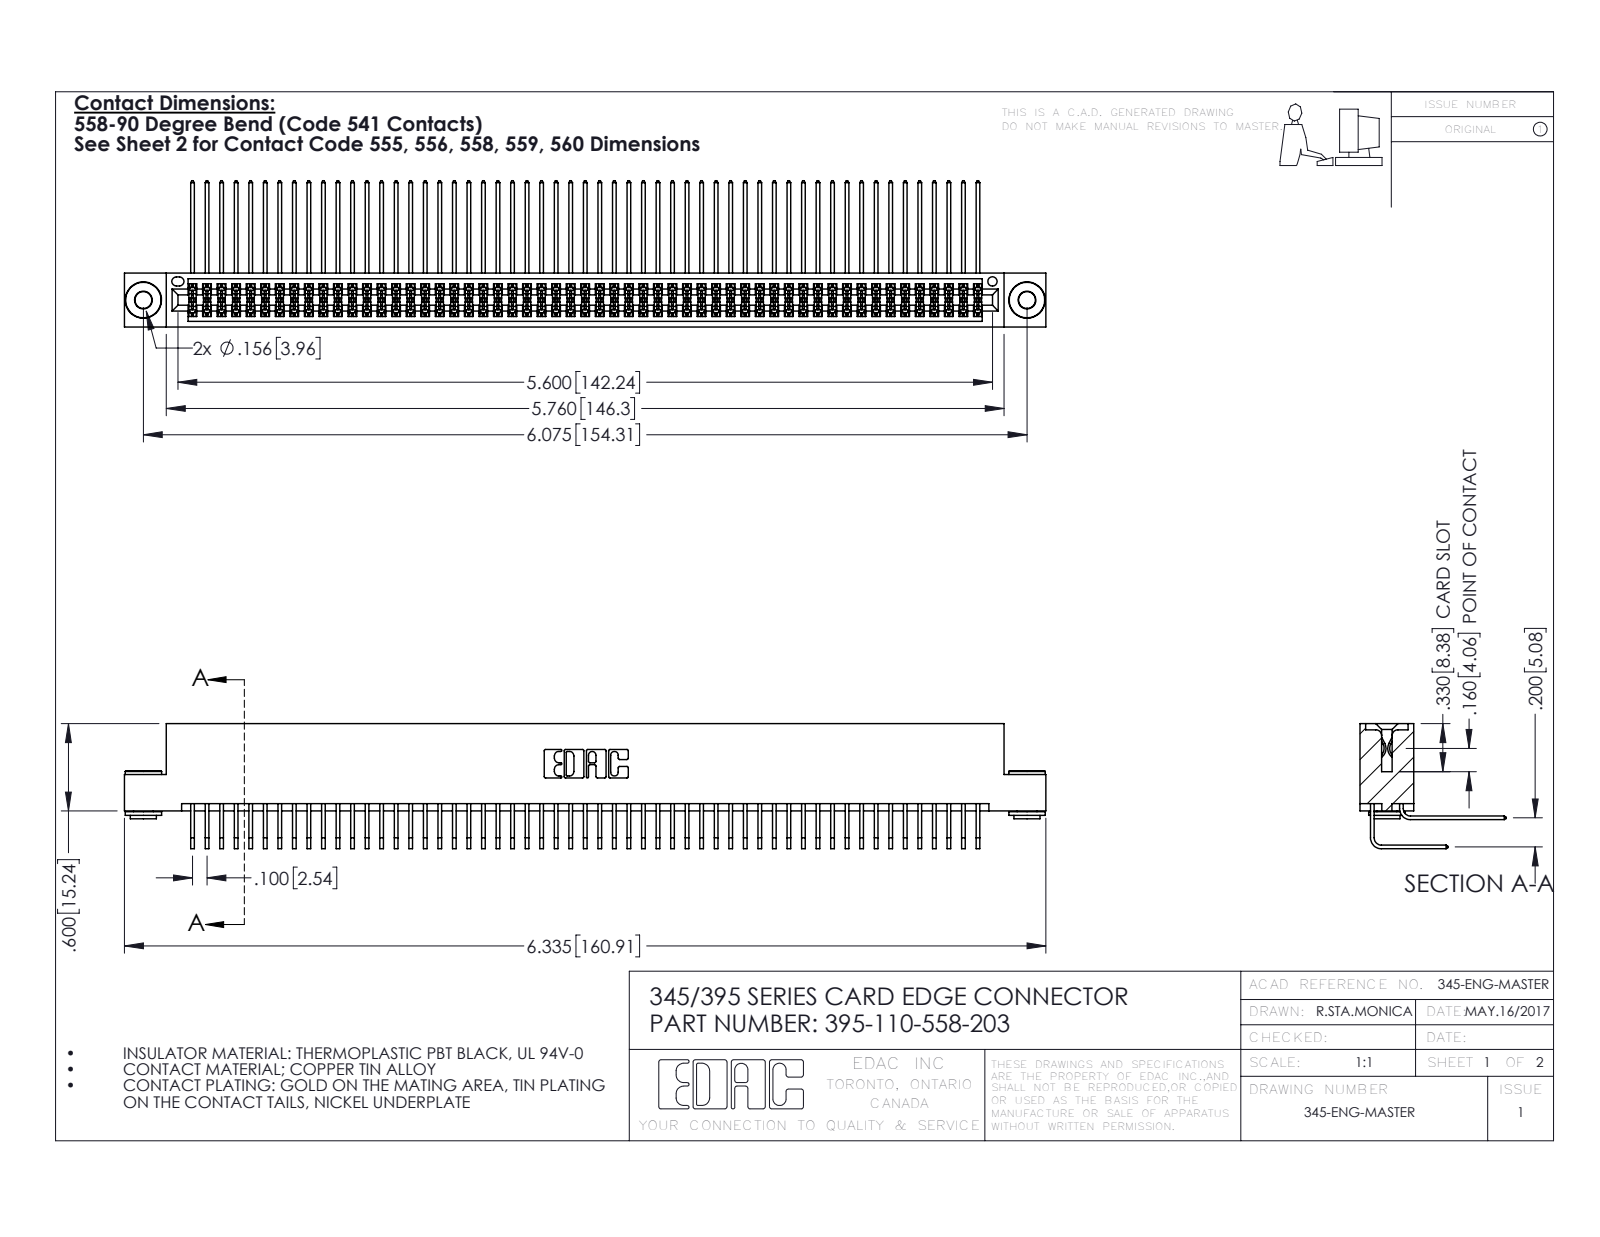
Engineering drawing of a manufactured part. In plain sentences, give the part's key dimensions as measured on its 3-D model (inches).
The part is named "345 Part_Flush Mounting Lugs - 0.156 Dia-TH; 345-292-001_558 Tail - 2; 395-110-558-203; 345-292-001_558 559 Tail - 1 (+1 more)". Its 3-D file was written by "SolidWorks 2016 (CONFIG_CONTROL_DESIGN)". It is 113 solids with 5884 faces: 3940 planar, 1936 cylindrical and 8 other. Overall it measures 6.335 by 1.005 by 0.859 inches. Its volume is 1.001 cubic inches and its surface area 42.92 square inches. Round holes: 2 of diameter 0.116, 2 of diameter 0.156, 1 of diameter 0.064. Round bosses or shafts: 2 of diameter 0.25, 2 of diameter 0.18, 2 of diameter 0.136. Partial cylindrical surfaces (rounded edges, fillets, slot ends): 165 of radius 0.006, 22 of radius 0.01, 6 of radius 0.007, 6 of radius 0.031, 3 of radius 0.026, 2 of radius 0.014, 2 of radius 0.019, 2 of radius 0.022. The main face-to-face distances are 0.072, 0.298, 0.2, 0.37, 0.025, 0.098, 0.272, 0.225, 0.025, 0.175. The hole center spacings are 0.27, 5.839, 6.075.
